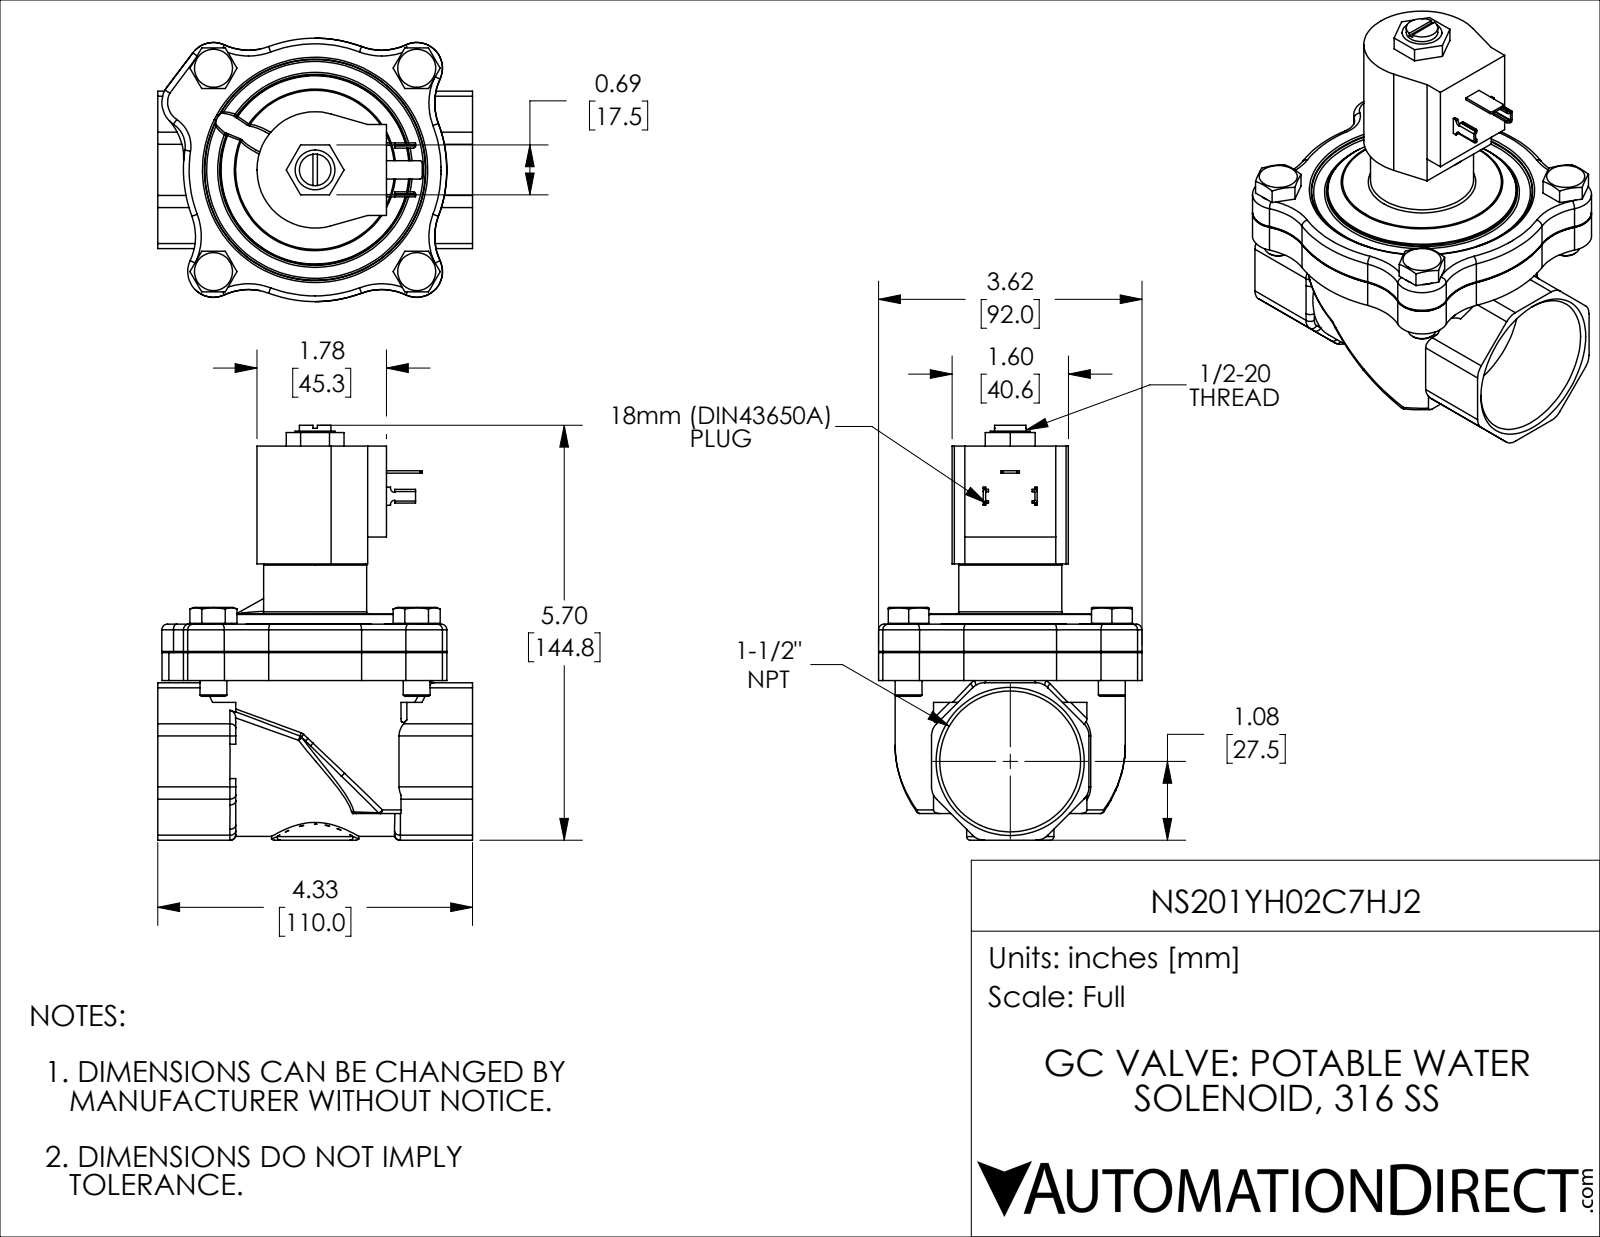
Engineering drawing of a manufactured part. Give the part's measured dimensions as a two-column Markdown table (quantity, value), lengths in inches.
| quantity | value |
| --- | --- |
| part name | NS201YH02C7HJ2 |
| STEP written by | SolidWorks 2024 (CONFIG_CONTROL_DESIGN) |
| units | inches |
| bodies | 12 solids, 541 faces (170 planar, 156 cylindrical, 215 other) |
| overall size | 5.701 × 4.33 × 3.622 |
| volume | 26.21 in³ |
| surface area | 138.4 in² |
| round holes (diameter × count) | 0.375 × 4, 0.433 × 4, 0.125 × 1, 0.488 × 1, 0.846 × 1, 0.949 × 1, 1.937 × 1 |
| round bosses / shafts (diameter × count) | 0.504 × 4, 0.37 × 4, 3.165 × 1, 1.417 × 1, 1.2 × 1, 0.547 × 1, 0.434 × 1 |
| partial cylindrical surfaces (radius × count) | 0.787 × 15, 0.08 × 13, 0.03 × 8, 0.236 × 8, 0.354 × 8, 0.362 × 2, 1.811 × 2, 0.031 × 1 |
| main face-to-face distances | 0.382, 0.775, 0.393, 3.222, 2.84, 2.447, 1.83, 1.602, 1.22, 0.827 |
| hole center spacings | 2.795, 1.976, 1.977, 2.794, 2.795, 3.952, 3.953 |
